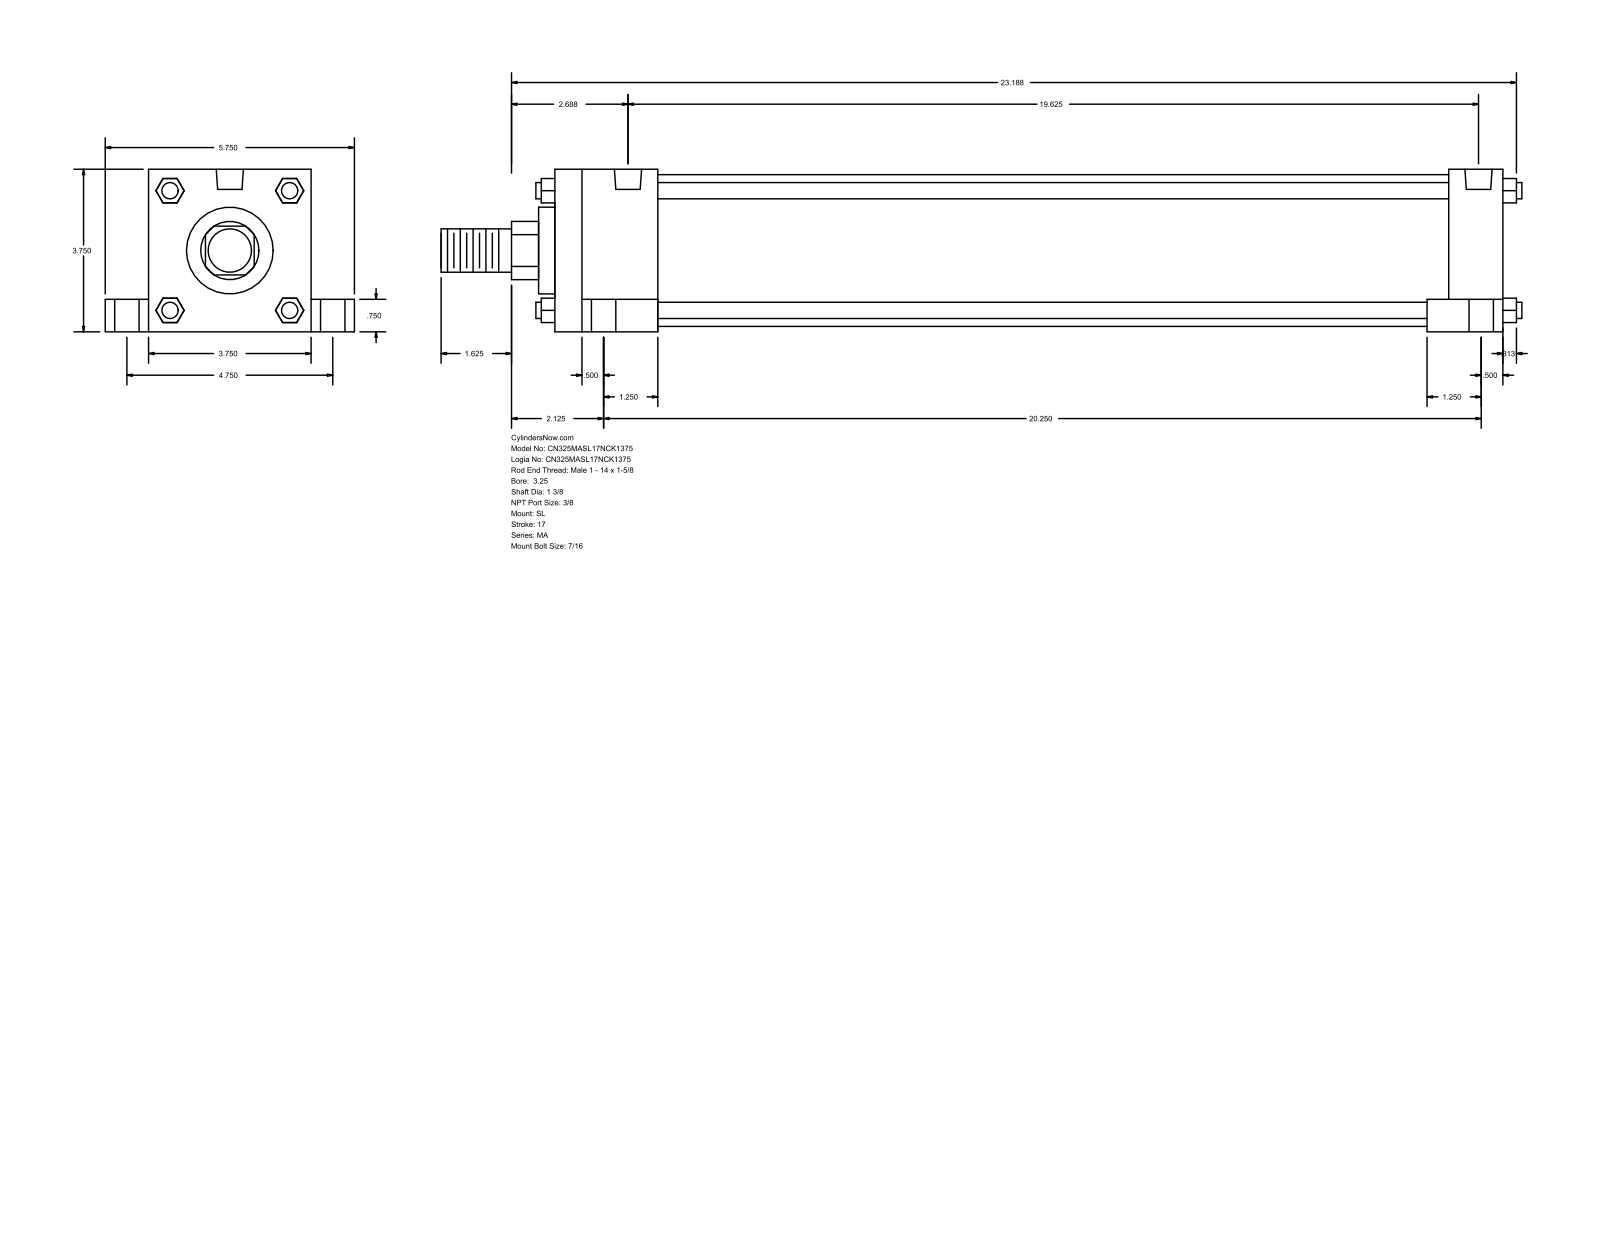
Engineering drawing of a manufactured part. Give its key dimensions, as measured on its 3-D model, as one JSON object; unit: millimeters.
{"part_name": "MA_SL__0325_1.375", "step_written_by": "GSSL Pune (CONFIG_CONTROL_DESIGN)", "units": "millimeters", "bodies": {"solids": 0, "faces": 148, "planar": 112, "cylindrical": 36, "other": 0}, "overall_size": [633.41, 146.05, 95.25], "round_holes": [[11.11, 4], [14.29, 4], [20.64, 4], [15.93, 2]], "round_bosses_or_shafts": [[9.53, 4], [88.9, 1], [50.8, 1], [34.92, 1], [25.4, 1]], "partial_cylinders_radius": [[17.06, 1]], "face_to_face_distances": [95.24, 555.62, 463.55, 25.41, 120.65, 523.87, 31.75, 60.32, 495.3, 19.05], "hole_center_spacings": [60.35, 60.66, 62, 63.27, 120.66, 488.95, 498.96, 503.7]}
